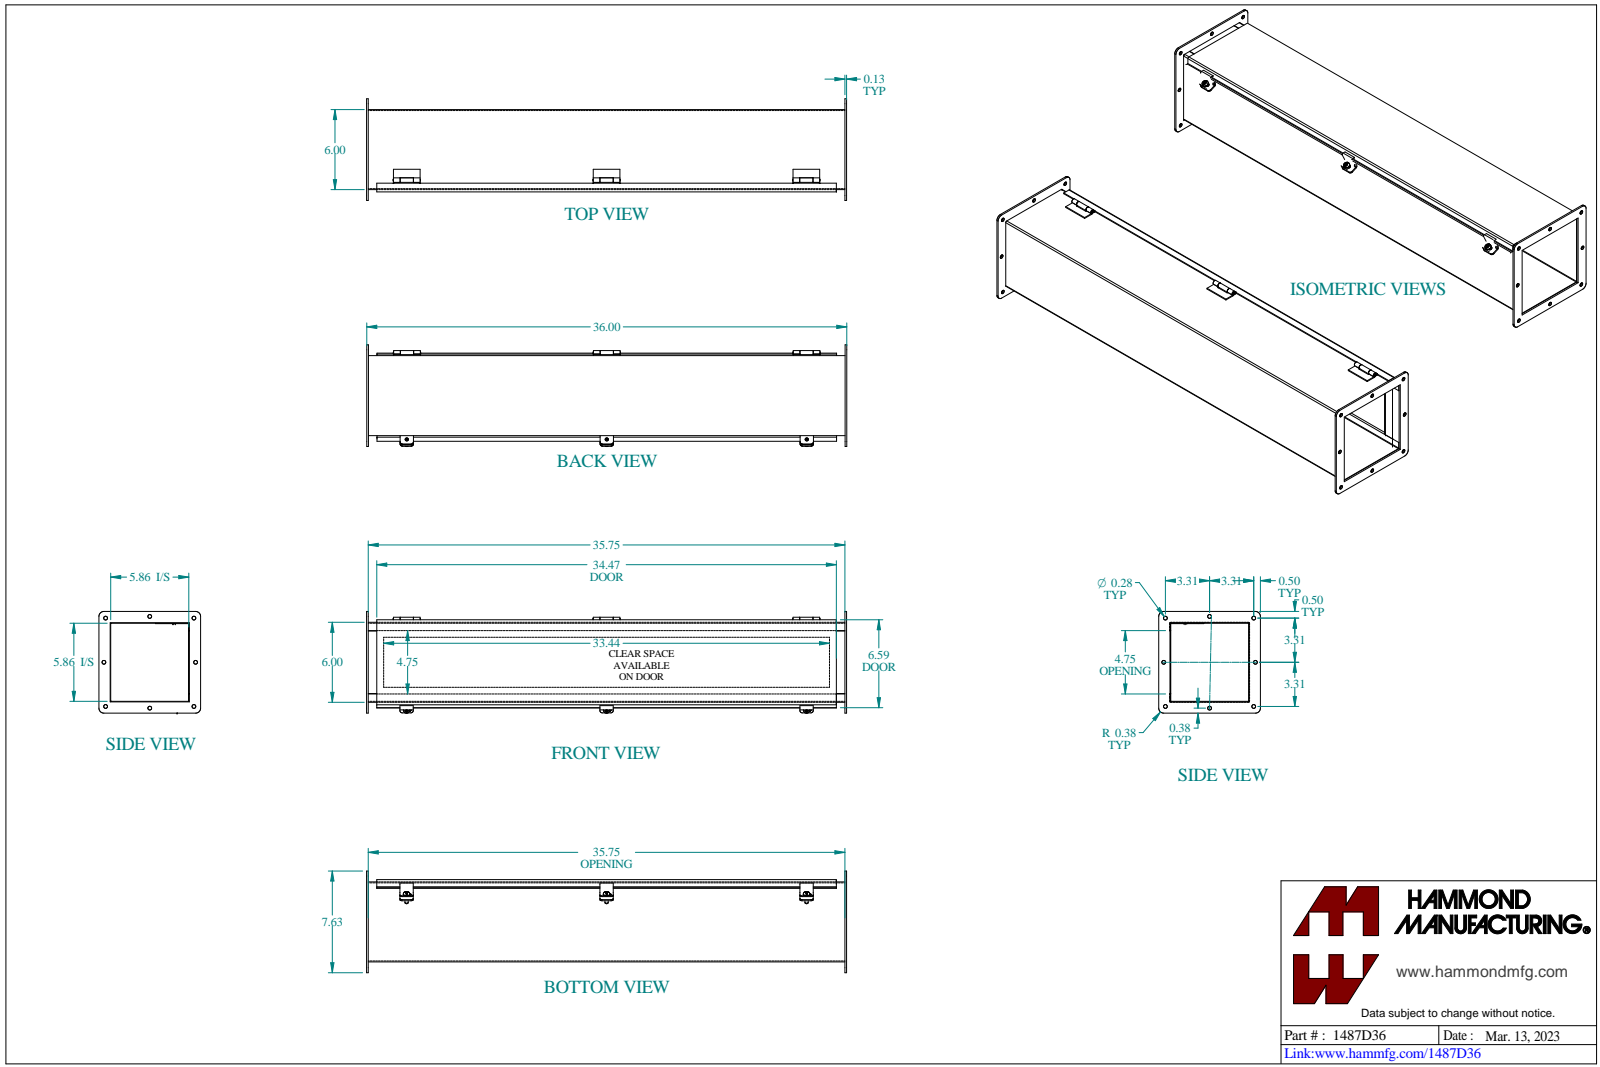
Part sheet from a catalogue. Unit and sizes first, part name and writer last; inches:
Units: inches
Overall size (bounding box): 36.125 × 7.629 × 7.625
Round holes (diameter × count): ⌀0.281 ×8, ⌀0.213 ×3, ⌀0.125 ×1
Round bosses / shafts (diameter × count): ⌀0.48 ×3, ⌀0.246 ×3, ⌀0.275 ×1, ⌀0.125 ×1
Partial cylindrical surfaces — rounded edges, fillets, slot ends (radius × count): R0.188 ×12, R0.036 ×7, R0.108 ×7, R0.01 ×6, R0.141 ×6, R0.25 ×4, R0.375 ×4, R0.029 ×2
Main face-to-face distances: 0.072, 5.928, 6.1, 6, 5.856, 6.028, 6.172, 0.172, 0.125, 0.1
Hole centre spacings: 7.519, 3.315, 3.315, 6.625, 4.861, 6.875, 9.369, 15
Volume: 78.64 in³ · Surface area: 2 128 in²
Bodies: 25 solids, 560 faces (299 planar, 204 cylindrical, 57 other)
Part name (STEP PRODUCT): 1487D36
STEP written by: SolidWorks 2023 (CONFIG_CONTROL_DESIGN)
